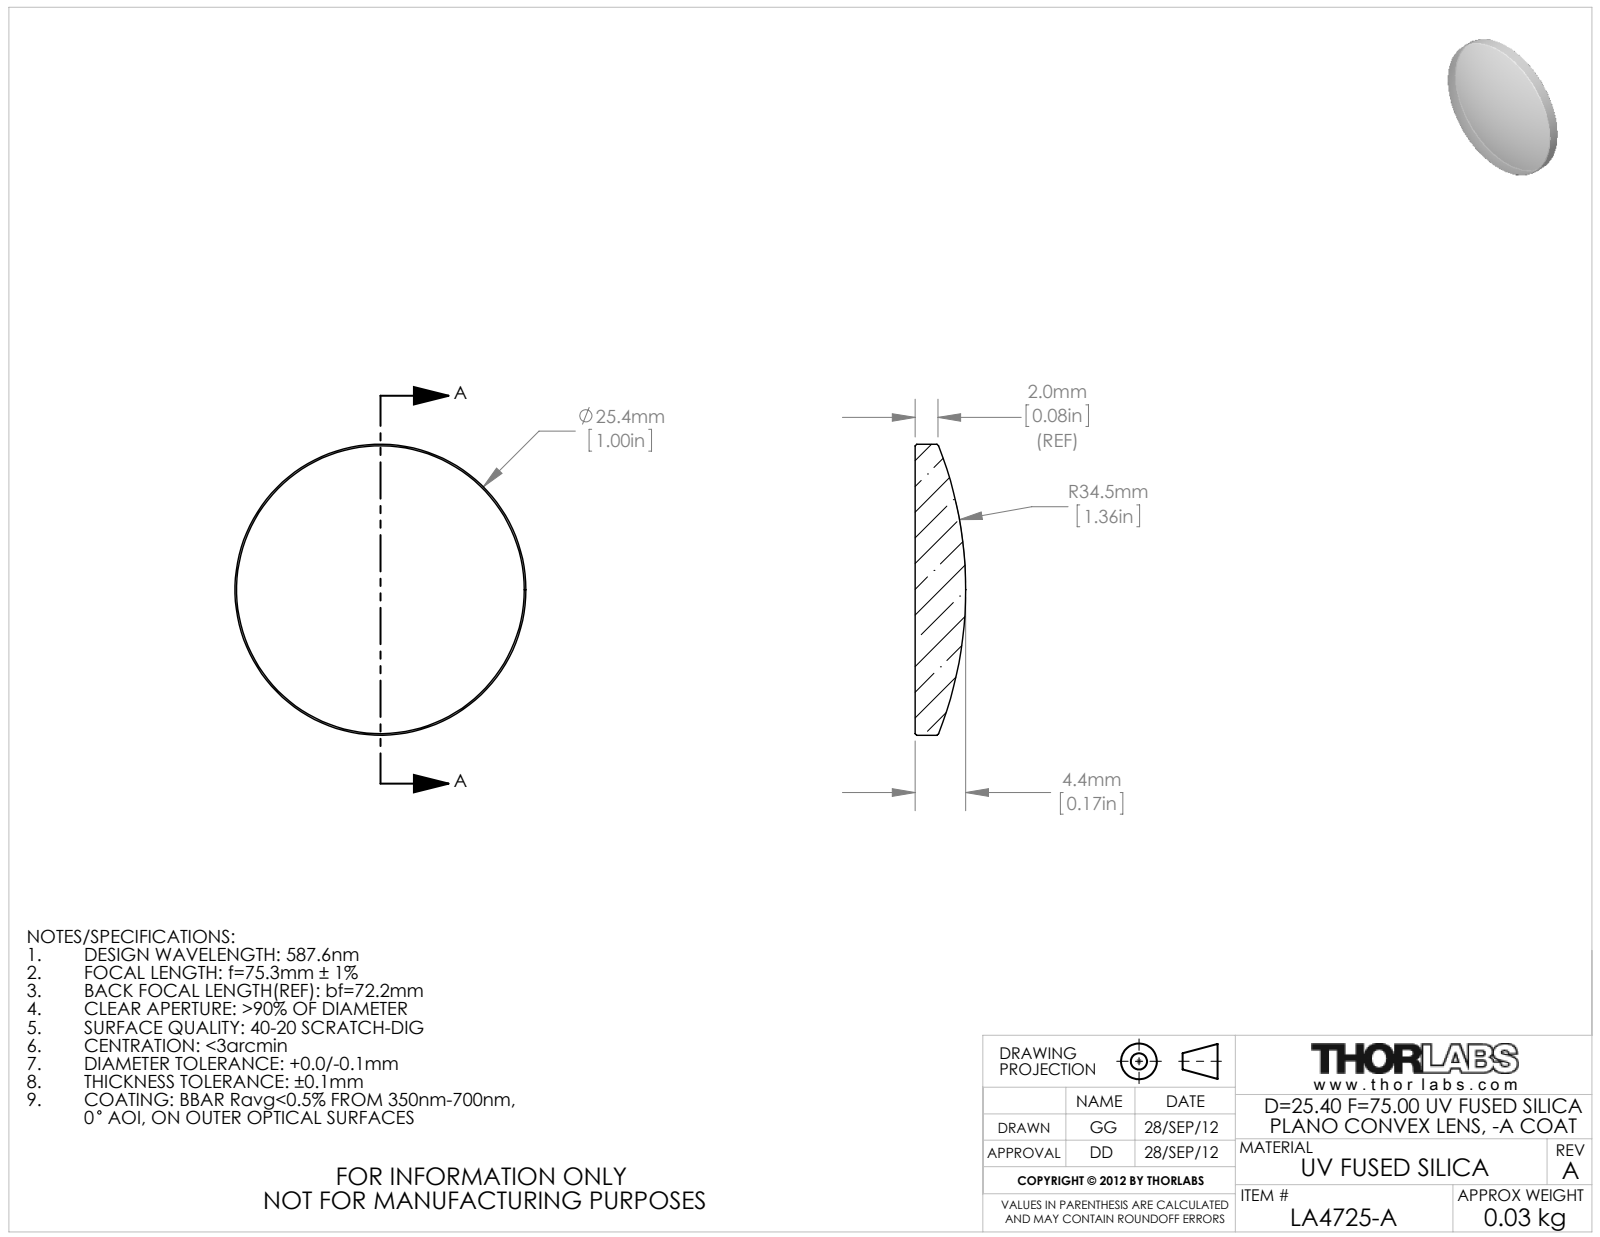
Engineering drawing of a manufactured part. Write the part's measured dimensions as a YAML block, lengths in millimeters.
part_name: "24984-E0W"
step_written_by: "SolidWorks 2011 (CONFIG_CONTROL_DESIGN)"
units: millimeters
bodies: {solids: 1, faces: 9, planar: 1, cylindrical: 2, other: 6}
overall_size: [25.4, 25.4, 4.42]
volume: 1633
surface_area: 1182
round_bosses_or_shafts:
  - {diameter: 25.4, count: 1}
